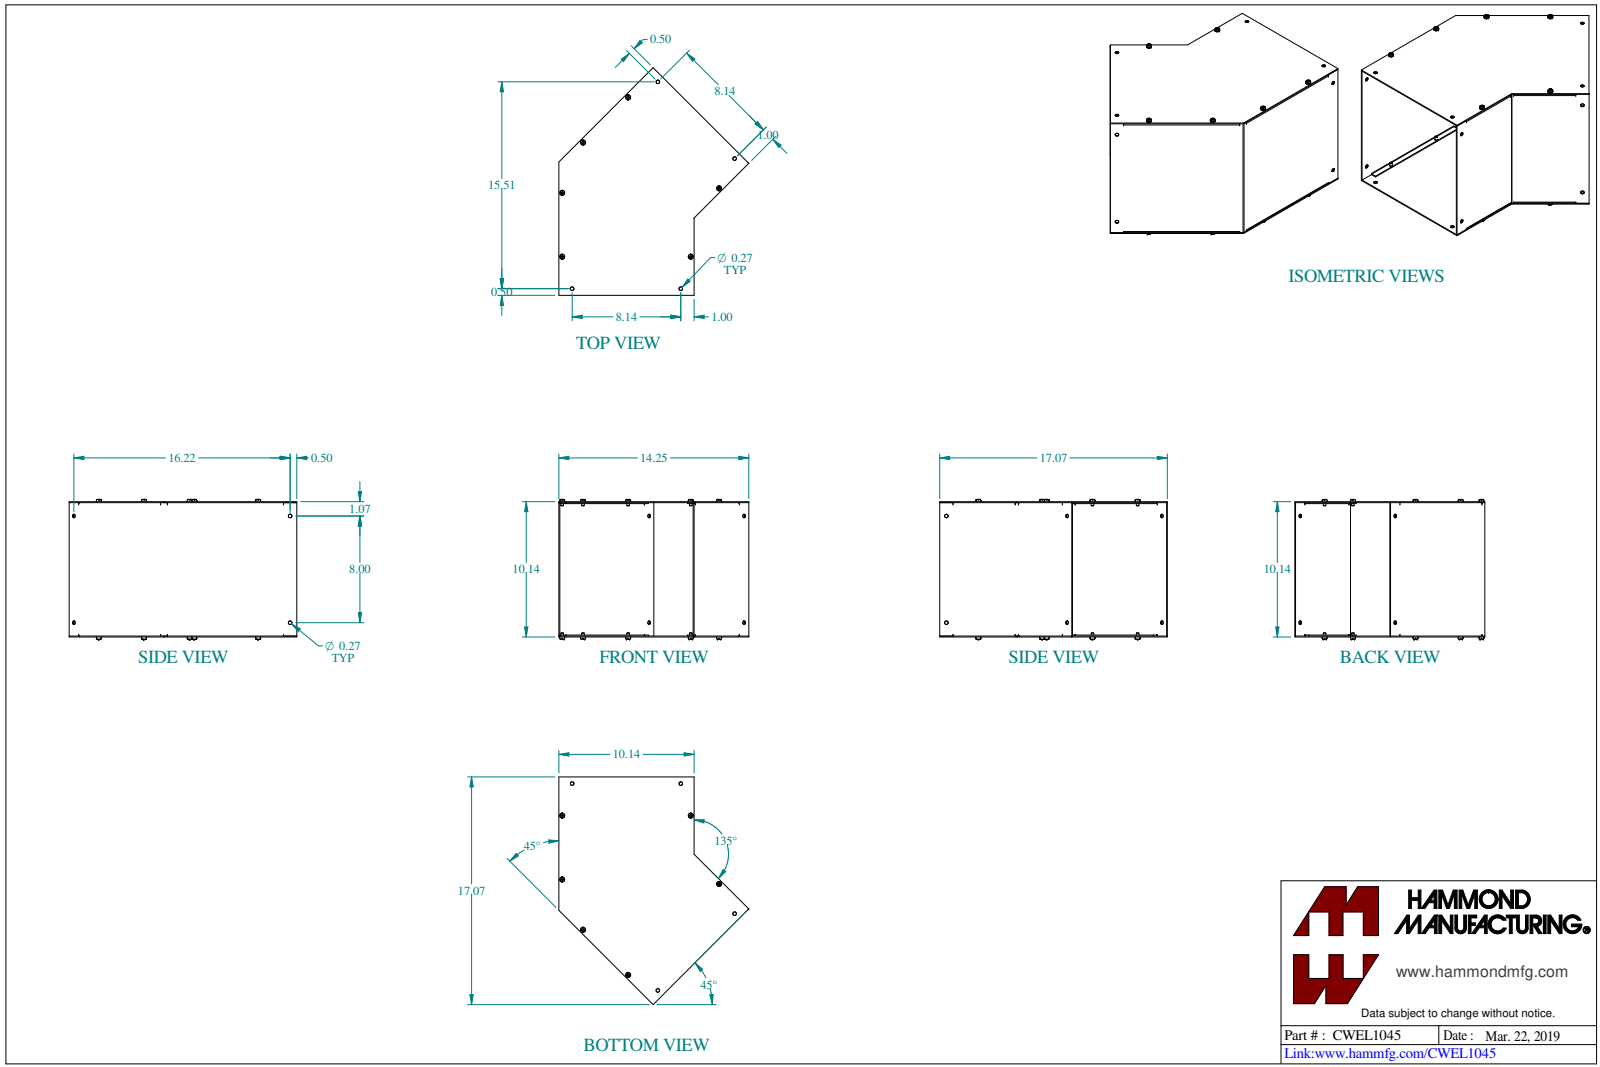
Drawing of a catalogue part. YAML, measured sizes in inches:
part_name: "CWEL1045"
step_written_by: "SolidWorks 2023 (CONFIG_CONTROL_DESIGN)"
units: inches
bodies: {solids: 16, faces: 536, planar: 316, cylindrical: 148, other: 72}
overall_size: [17.071, 14.247, 10.494]
volume: 47.52
surface_area: 1337
round_holes:
  - {diameter: 0.266, count: 10}
  - {diameter: 0.17, count: 6}
  - {diameter: 0.25, count: 6}
round_bosses_or_shafts:
  - {diameter: 0.19, count: 6}
  - {diameter: 0.375, count: 5}
  - {diameter: 0.375, count: 1}
partial_cylinders:
  - {radius: 0.036, count: 10}
  - {radius: 0.108, count: 10}
face_to_face_distances: [0.072, 10.072, 10, 10.144, 10.139, 10.067, 9.995, 10.067, 0.072, 0.144]
hole_center_spacings: [9.644, 8, 9.212, 10.767, 11.772, 2.513, 2.514, 4.789]
